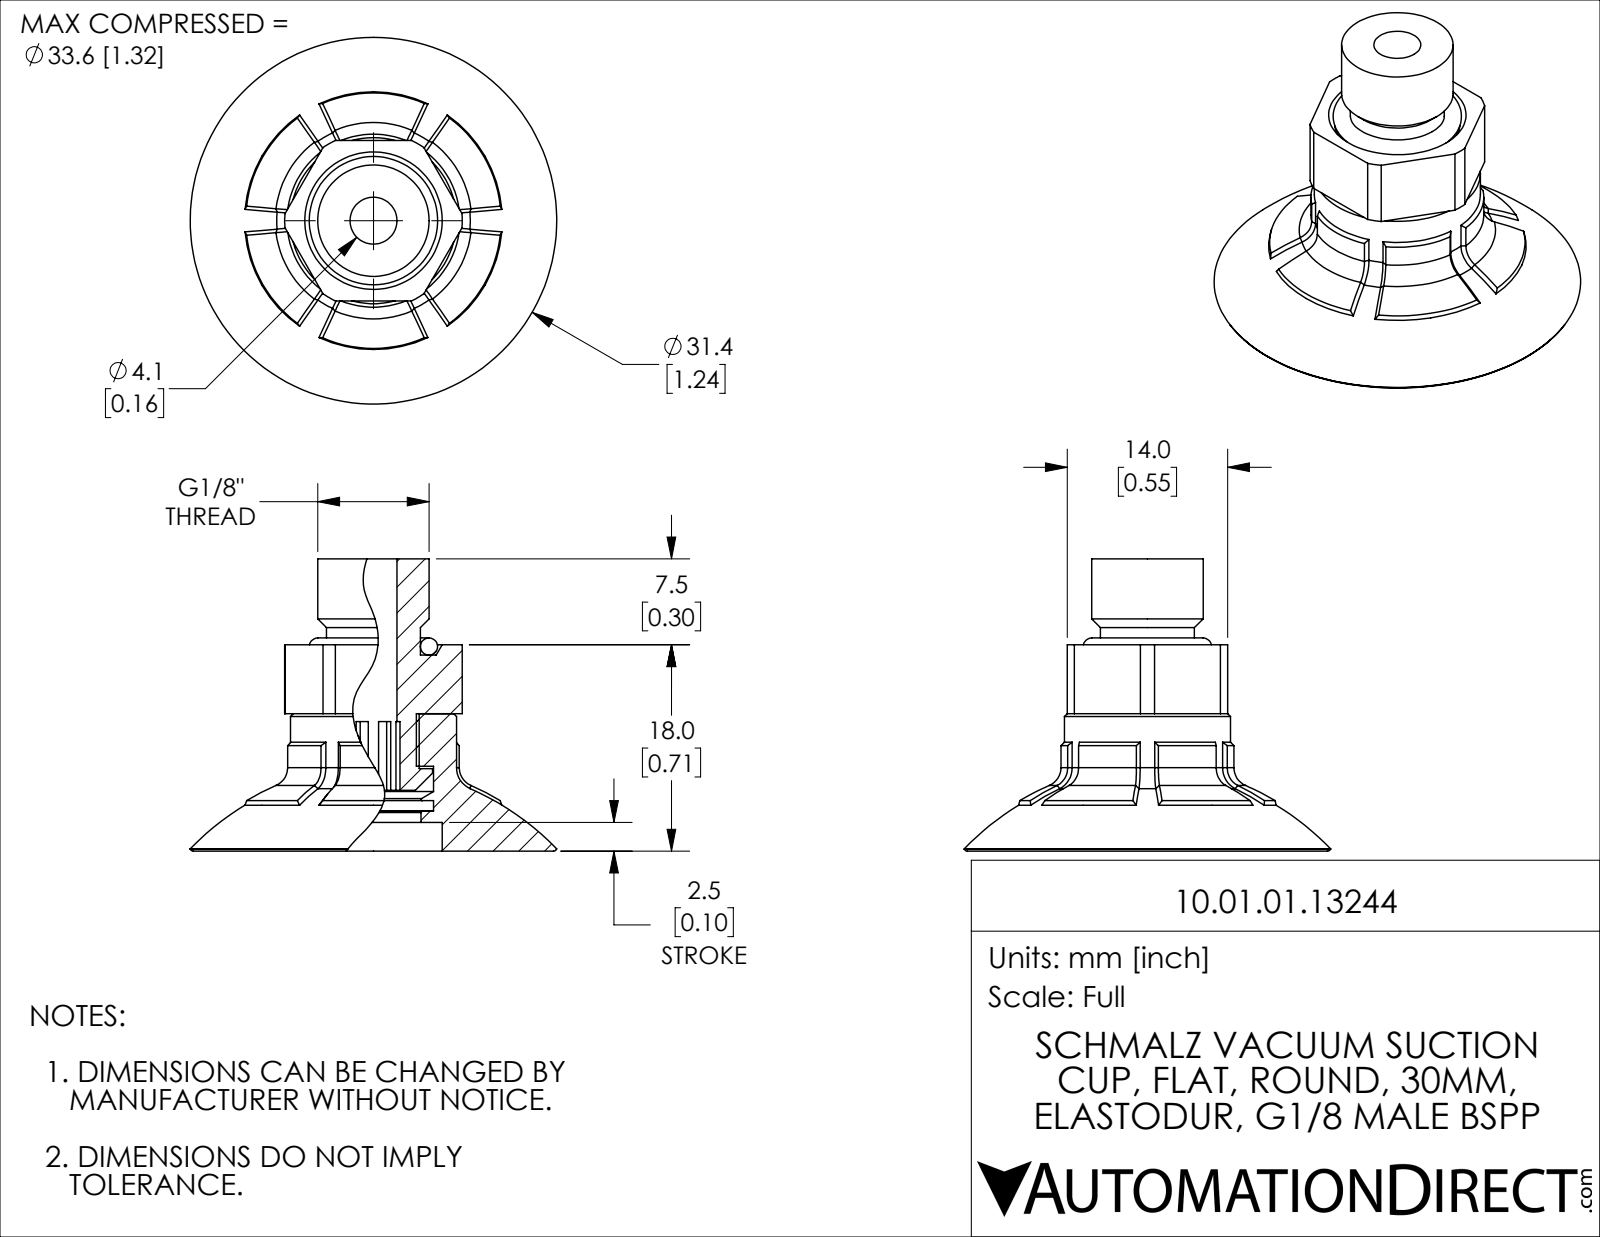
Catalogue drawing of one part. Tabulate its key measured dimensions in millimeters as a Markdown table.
| quantity | value |
| --- | --- |
| part name | 10.01.01.13244 |
| STEP written by | SolidWorks 2021 (CONFIG_CONTROL_DESIGN) |
| units | millimeters |
| bodies | 3 solids, 182 faces (47 planar, 35 cylindrical, 100 other) |
| overall size | 32 × 32 × 25.5 |
| volume | 4 887 mm³ |
| surface area | 3 930 mm² |
| round holes (diameter × count) | 4.1 × 1, 7.5 × 1, 8.3 × 1, 10.5 × 1, 12 × 1 |
| round bosses / shafts (diameter × count) | 14.5 × 1, 10.3 × 1, 9.73 × 1, 8.2 × 1, 8 × 1 |
| partial cylindrical surfaces (radius × count) | 7.55 × 1, 7.75 × 1 |
| main face-to-face distances | 12, 14, 0.9, 25.5, 13.5, 2.5, 9.5, 23, 1.9, 2.8 |
